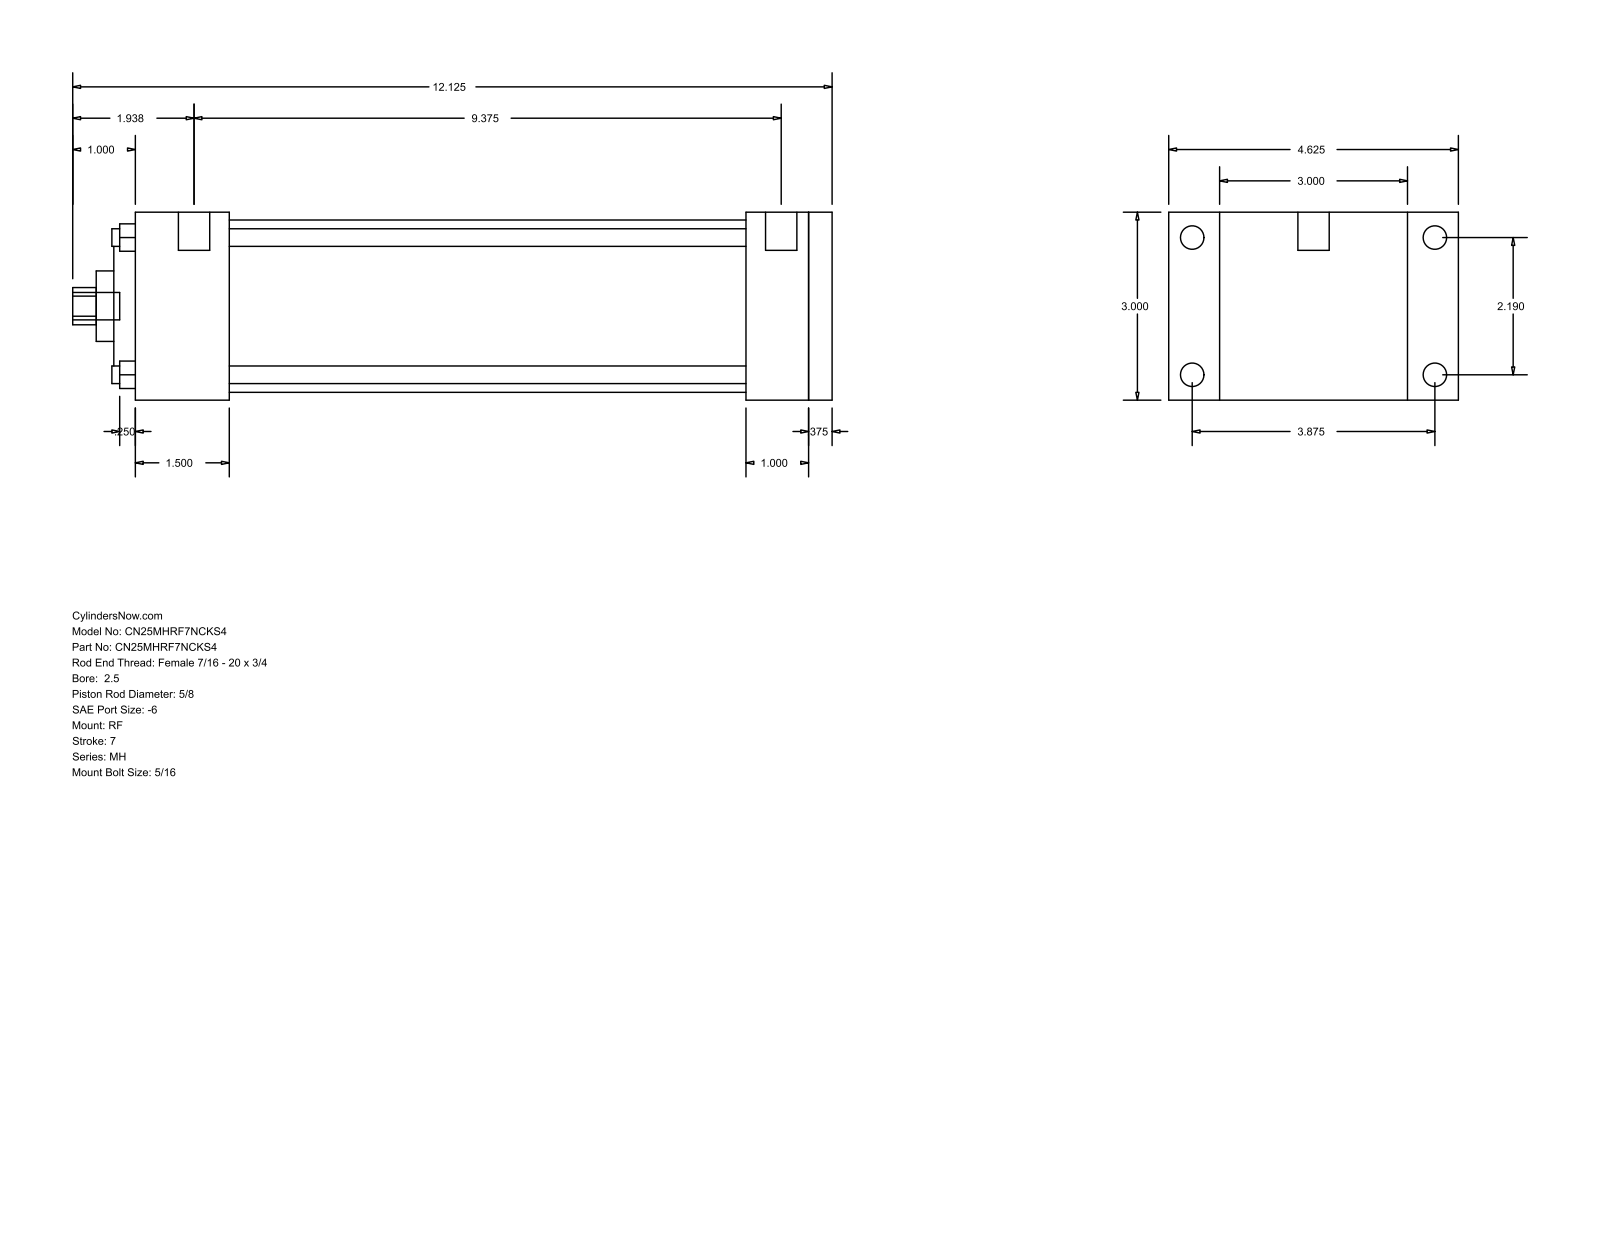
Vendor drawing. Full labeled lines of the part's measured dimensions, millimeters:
Part name (STEP PRODUCT): MH_RF__0250_0.625
STEP written by: GSSL Pune (CONFIG_CONTROL_DESIGN)
Units: millimetres
Bodies: 0 solids, 94 faces (65 planar, 29 cylindrical, 0 other)
Overall size (bounding box): 307.98 × 117.47 × 76.2
Round holes (diameter × count): ⌀7.14 ×4, ⌀15.88 ×1, ⌀28.57 ×1, ⌀55.55 ×1, ⌀69.85 ×1
Round bosses / shafts (diameter × count): ⌀9.53 ×4, ⌀5.56 ×4, ⌀12.7 ×2, ⌀11.11 ×1
Partial cylindrical surfaces — rounded edges, fillets, slot ends (radius × count): R7.54 ×1
Main face-to-face distances: 76.2, 9.53, 282.58, 273.05, 25.4, 247.65, 34.93, 38.1, 209.55, 234.95
Hole centre spacings: 39.33, 55.62, 78.66
